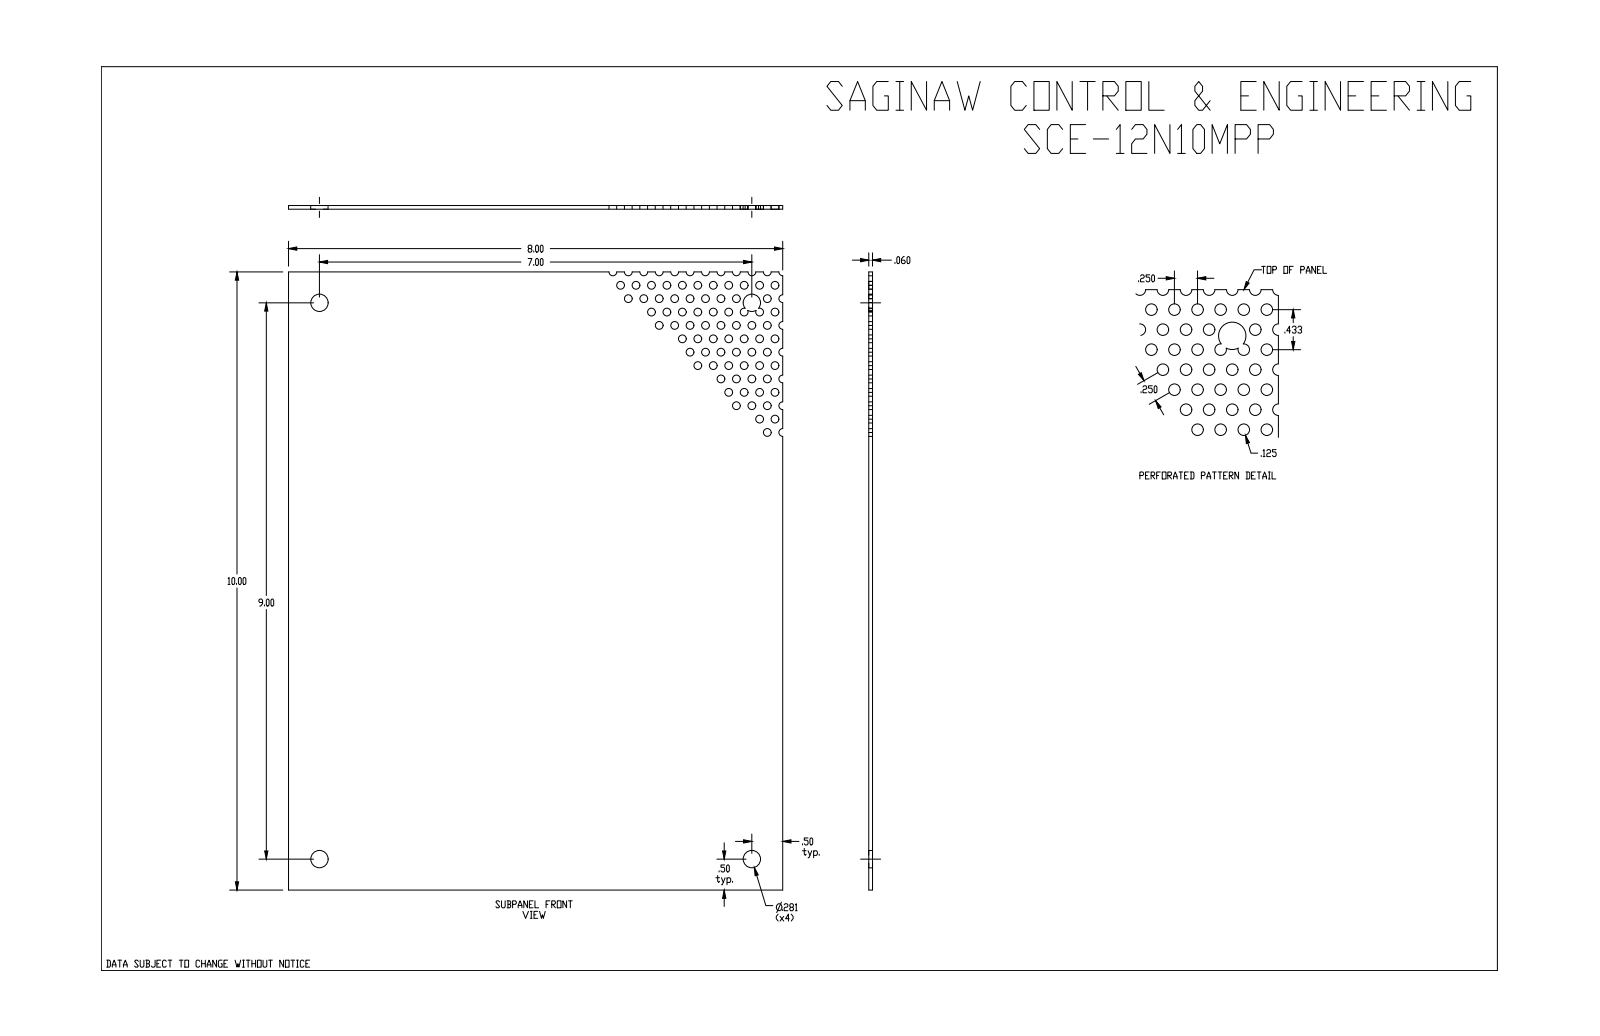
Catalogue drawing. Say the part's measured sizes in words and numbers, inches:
The part is named "SCE-12N10MPP". Its 3-D file was written by "SolidWorks 2019 (CONFIG_CONTROL_DESIGN)". It is 1 solid with 116 faces: 23 planar, 93 cylindrical and 0 other. Overall it measures 10 by 8 by 0.06 inches. Its volume is 4.727 cubic inches and its surface area 161.7 square inches. Round holes: 55 of diameter 0.125, 15 of diameter 0.125, 4 of diameter 0.281. Partial cylindrical surfaces (rounded edges, fillets, slot ends): 13 of radius 0.063, 5 of radius 0.062. The main face-to-face distances are 0.06, 8, 10. The hole center spacings are 0.25, 0.661, 0.5, 0.433, 0.433, 1.323, 1.09, 0.75.
